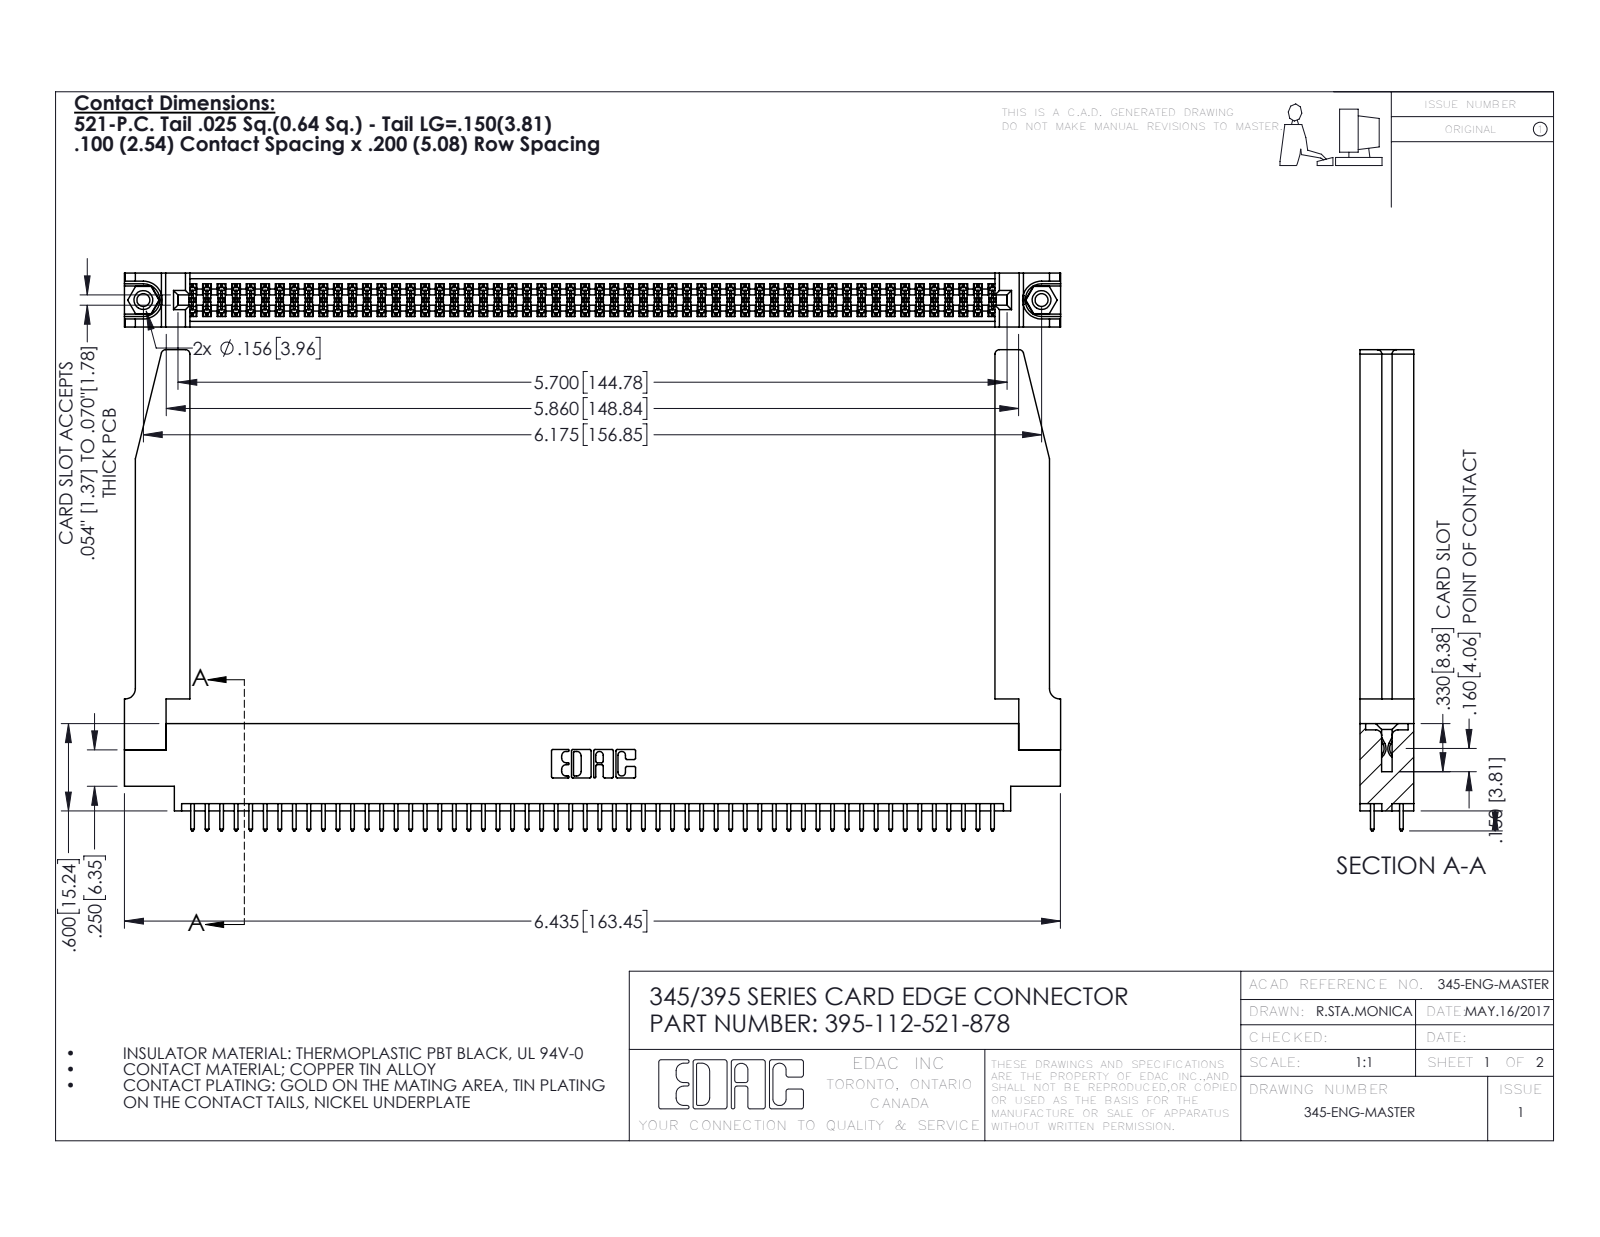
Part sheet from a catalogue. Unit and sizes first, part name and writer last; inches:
Units: inches
Overall size (bounding box): 6.436 × 3.307 × 0.37
Round holes (diameter × count): ⌀0.089 ×2, ⌀0.125 ×2, ⌀0.156 ×2, ⌀0.064 ×1
Round bosses / shafts (diameter × count): ⌀0.155 ×2
Partial cylindrical surfaces — rounded edges, fillets, slot ends (radius × count): R0.006 ×168, R0.01 ×112, R0.01 ×22, R0.03 ×8, R0.007 ×6, R0.031 ×6, R0.026 ×3, R0.014 ×2
Main face-to-face distances: 0.072, 0.298, 0.37, 0.098, 0.272, 0.025, 0.2, 0.225, 0.175, 0.148
Hole centre spacings: 0.27, 5.939, 6.175
Volume: 1.441 in³ · Surface area: 47.1 in²
Bodies: 117 solids, 5964 faces (3922 planar, 1990 cylindrical, 52 other)
Part name (STEP PRODUCT): 345-250-001_345-250-001-102; 345-292-001_345-293-121; 395-112-521-878; 345-220-078_345-220-078 (+1 more)
STEP written by: SolidWorks 2016 (CONFIG_CONTROL_DESIGN)
